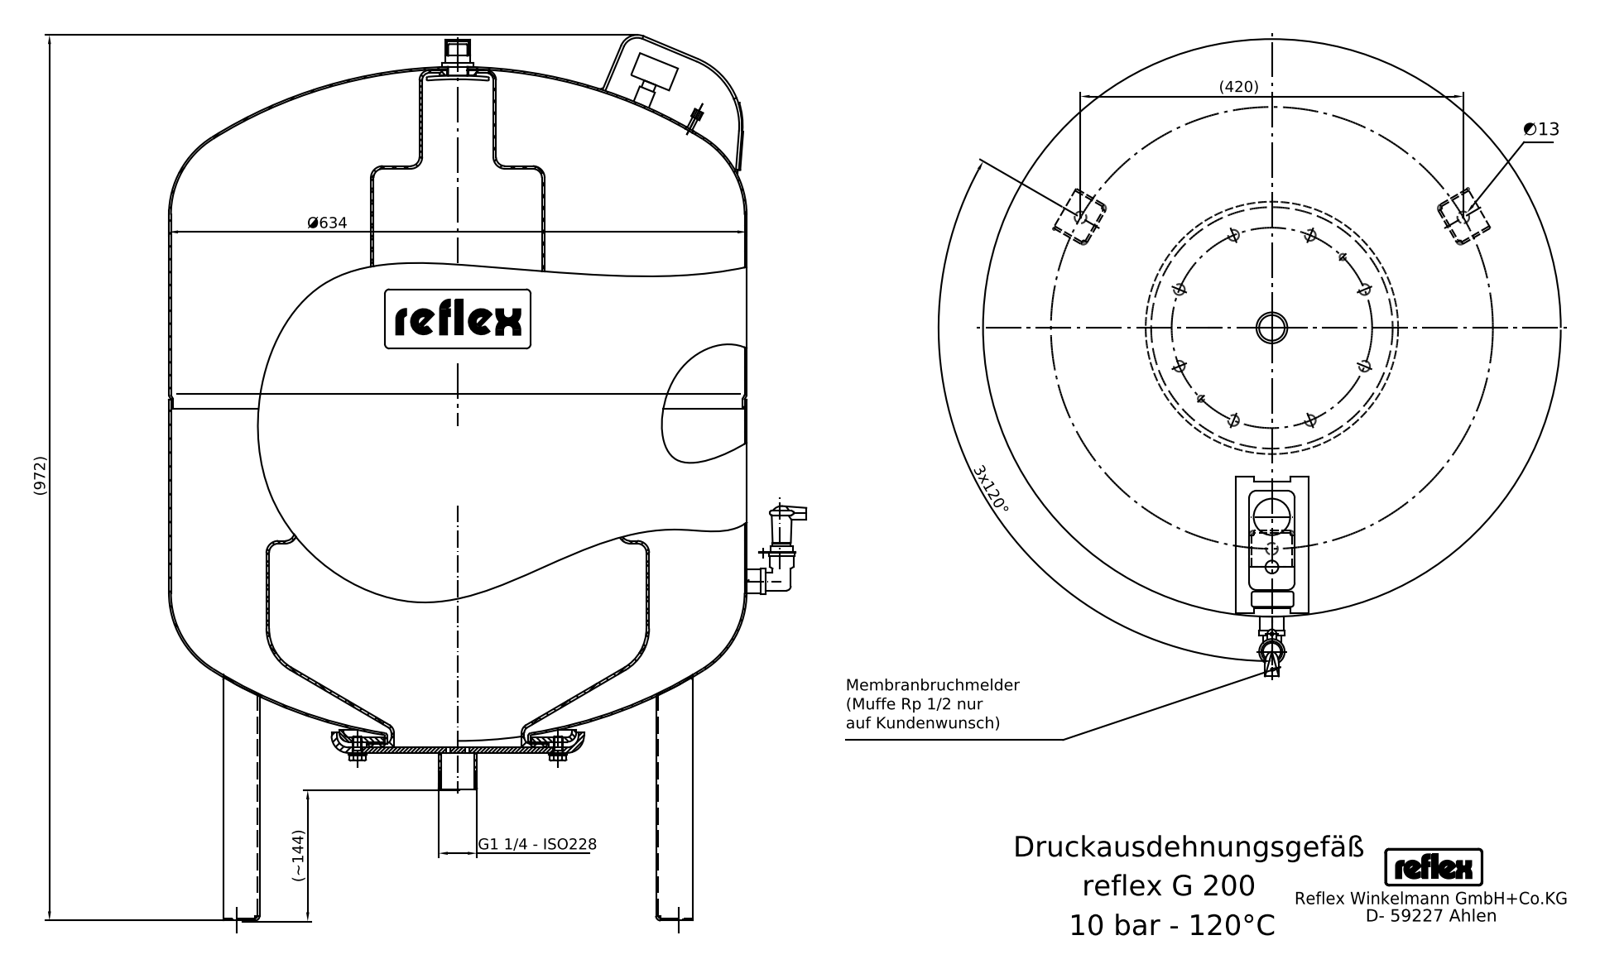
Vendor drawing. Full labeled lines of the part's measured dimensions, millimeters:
STEP written by: Mechanical Desktop 2008 (CONFIG_CONTROL_DESIGN)
Units: millimetres
Bodies: 21 solids, 513 faces (227 planar, 188 cylindrical, 98 other)
Overall size (bounding box): 967.4 × 699 × 635.14
Volume: 199 500 000 mm³ · Surface area: 3 469 000 mm²
Round holes (diameter × count): ⌀13.4 ×3, ⌀2.48 ×1, ⌀3.8 ×1, ⌀4.3 ×1, ⌀4.4 ×1, ⌀5.45 ×1, ⌀7 ×1, ⌀8 ×1, ⌀10 ×1, ⌀11.4 ×1, ⌀157 ×1, ⌀250 ×1
Round bosses / shafts (diameter × count): ⌀10 ×9, ⌀28 ×2, ⌀26 ×2, ⌀20 ×2, ⌀634 ×1, ⌀260 ×1, ⌀230 ×1, ⌀62 ×1
Partial cylindrical surfaces — rounded edges, fillets, slot ends (radius × count): R1 ×15, R2.5 ×15, R5 ×15, R3.94 ×4, R1.57 ×3, R2.69 ×2, R4.72 ×2, R6.49 ×2
Main face-to-face distances: 416, 2.5, 47.5, 169, 585, 6, 175, 591, 50, 45
Hole centre spacings: 242.5, 420.02, 297.88, 332.5, 575
